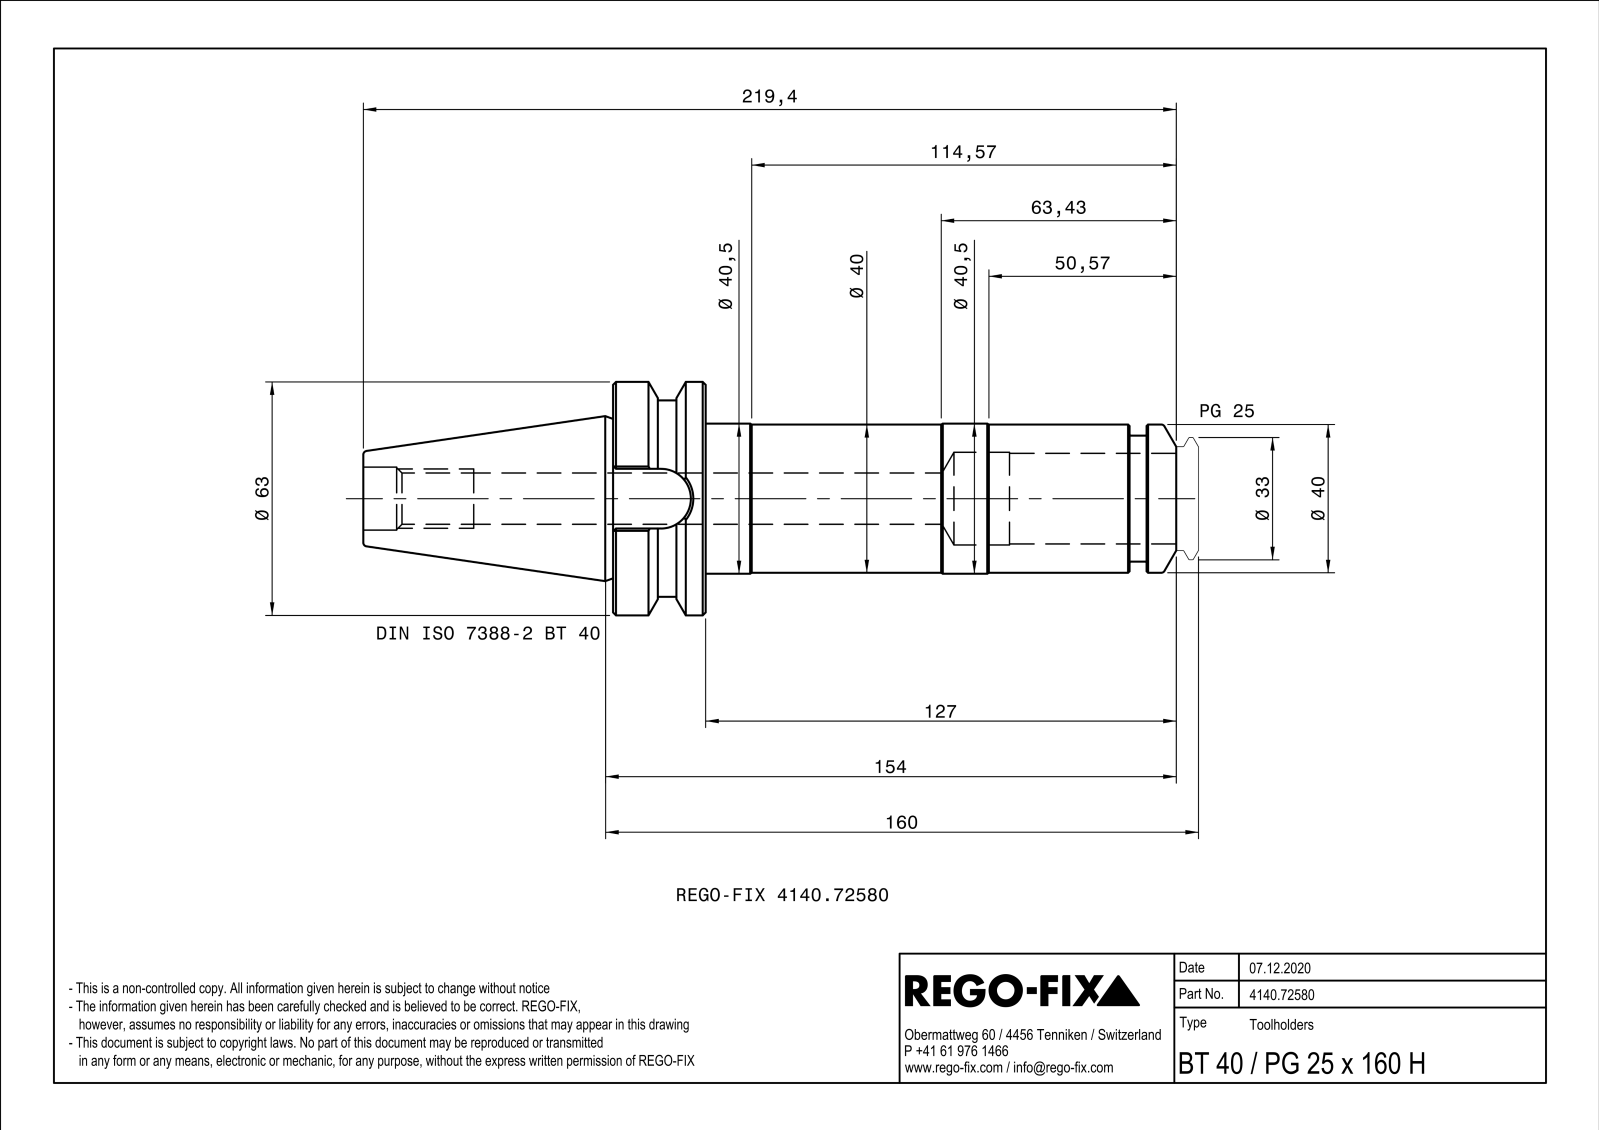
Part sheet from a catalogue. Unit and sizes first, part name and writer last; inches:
Units: inches
Overall size (bounding box): 8.638 × 2.48 × 2.48
Round holes (diameter × count): ⌀0.545 ×1, ⌀0.669 ×1, ⌀0.984 ×1
Round bosses / shafts (diameter × count): ⌀2.48 ×1, ⌀2.087 ×1, ⌀1.594 ×1, ⌀1.575 ×1, ⌀1.339 ×1
Partial cylindrical surfaces — rounded edges, fillets, slot ends (radius × count): R0.02 ×4, R0.317 ×1
Main face-to-face distances: 0.984, 1.776, 4.504, 5.488, 0.181, 4.685, 5.669, 8.323, 8.142, 3.638
Volume: 14.5 in³ · Surface area: 71.42 in²
Bodies: 1 solid, 112 faces (39 planar, 25 cylindrical, 48 other)
Part name (STEP PRODUCT): NOCUT
STEP written by: SIEMENS PLM Software Solid Edge ST10 (AUTOMOTIVE_DESIGN)
